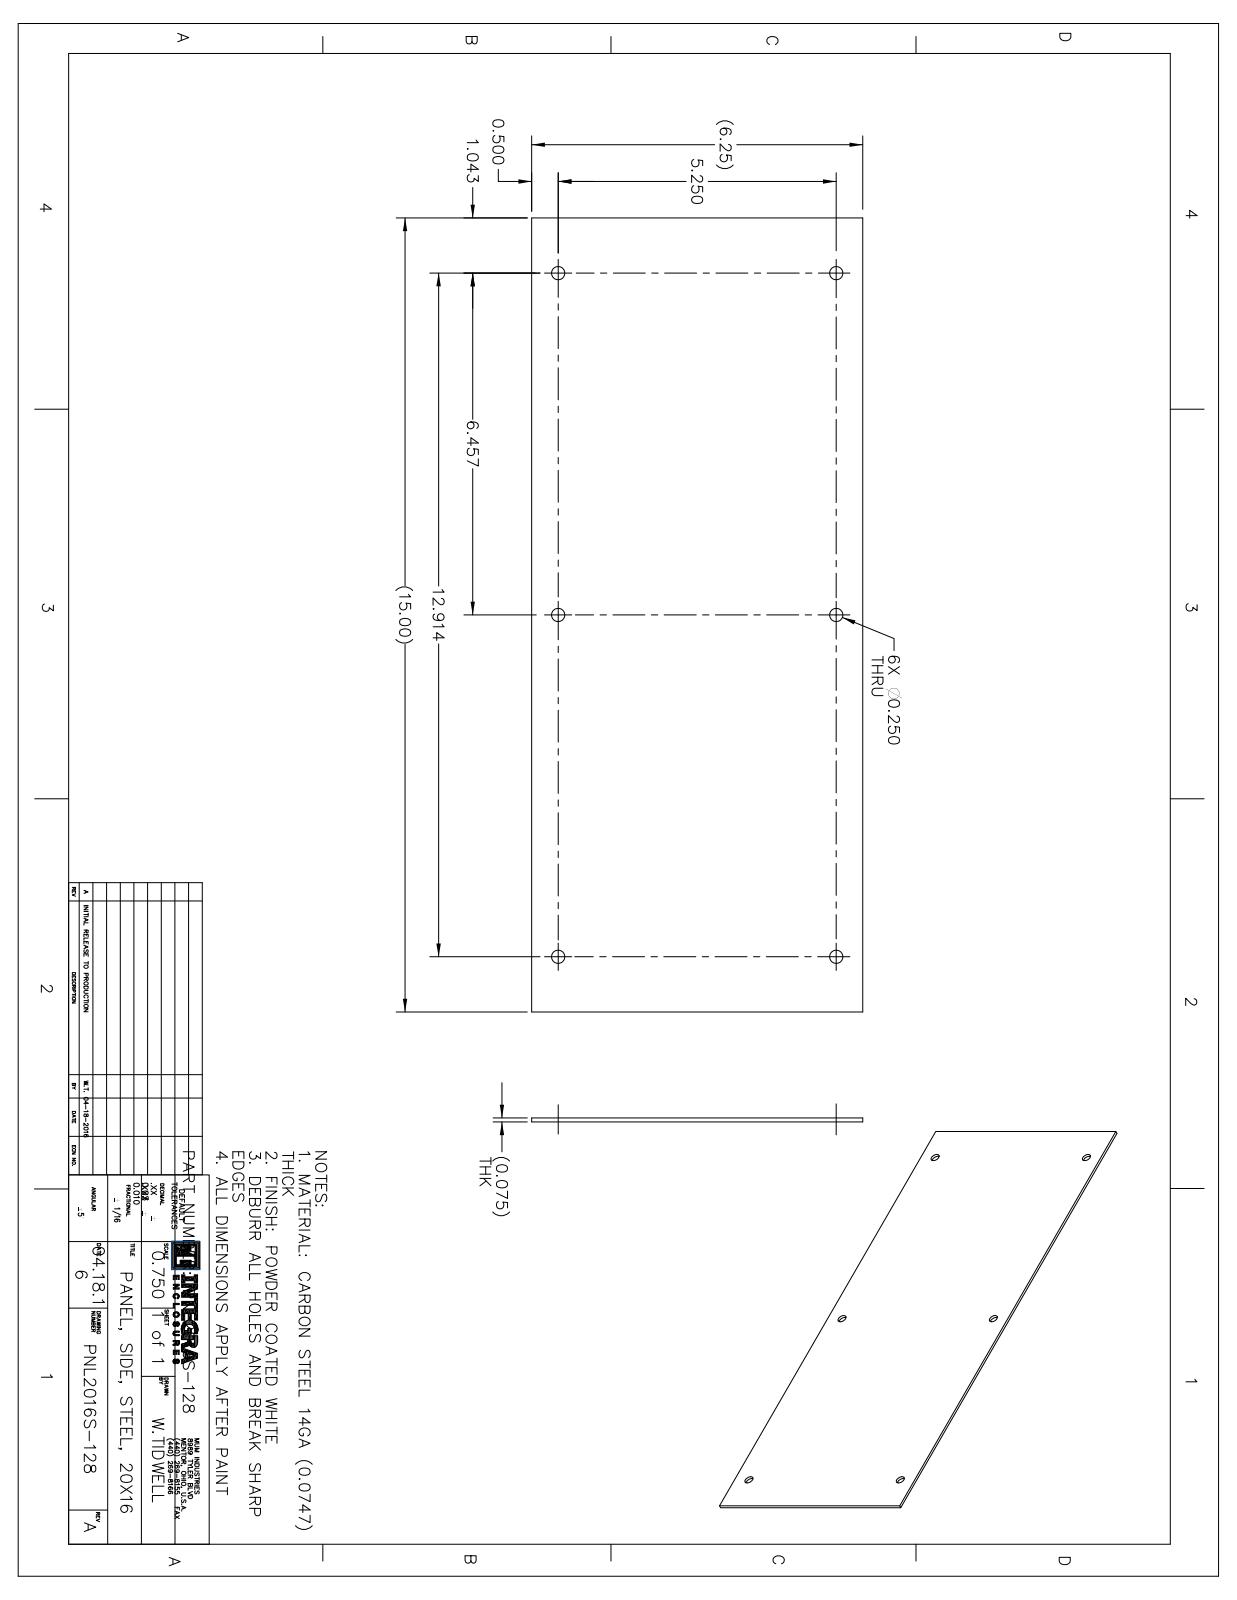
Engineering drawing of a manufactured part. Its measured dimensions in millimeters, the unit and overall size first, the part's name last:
Units: millimetres
Overall size (bounding box): 381 × 158.8 × 2
Round holes (diameter × count): ⌀6.4 ×6
Main face-to-face distances: 2, 158.8, 381
Hole centre spacings: 164, 211.4, 133.4, 328, 354.1
Volume: 122 500 mm³ · Surface area: 123 000 mm²
Bodies: 1 solid, 12 faces (6 planar, 6 cylindrical, 0 other)
Part name (STEP PRODUCT): SSP-2016-P10
STEP written by: SolidWorks 2018 (AUTOMOTIVE_DESIGN)
